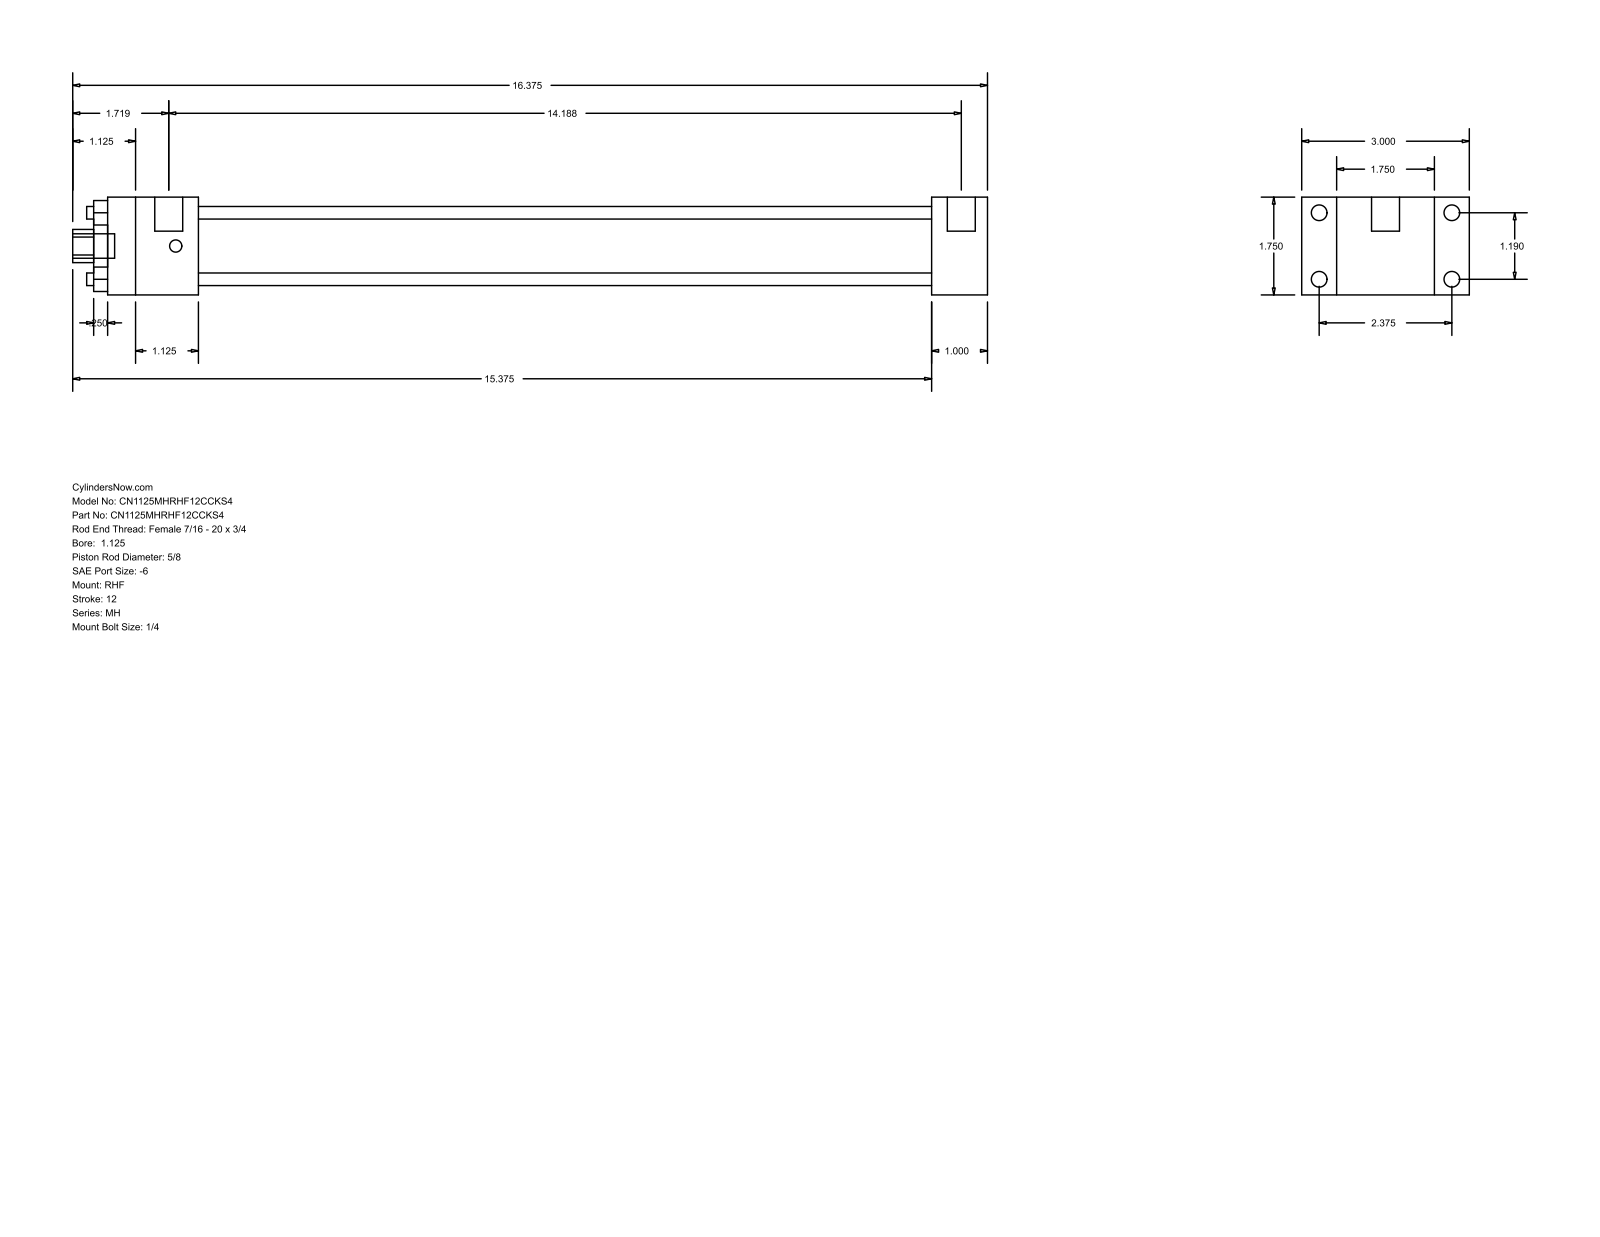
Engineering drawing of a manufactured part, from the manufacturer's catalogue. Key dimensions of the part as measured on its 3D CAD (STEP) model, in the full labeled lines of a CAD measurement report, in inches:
Part name (STEP PRODUCT): MH_RHF__0112_0.625
STEP written by: GSSL Pune (CONFIG_CONTROL_DESIGN)
Units: inches
Bodies: 0 solids, 88 faces (60 planar, 28 cylindrical, 0 other)
Overall size (bounding box): 16.375 × 3 × 1.75
Round holes (diameter × count): ⌀0.225 ×4, ⌀0.625 ×1, ⌀1.125 ×1, ⌀1.375 ×1
Round bosses / shafts (diameter × count): ⌀0.281 ×4, ⌀0.219 ×4, ⌀0.5 ×2, ⌀0.437 ×1
Partial cylindrical surfaces — rounded edges, fillets, slot ends (radius × count): R0.297 ×1
Main face-to-face distances: 1.75, 0.625, 2.375, 1, 3, 13.125, 14.125, 1.625, 14.75, 15.75
Hole centre spacings: 0.841, 1.19, 1.683
